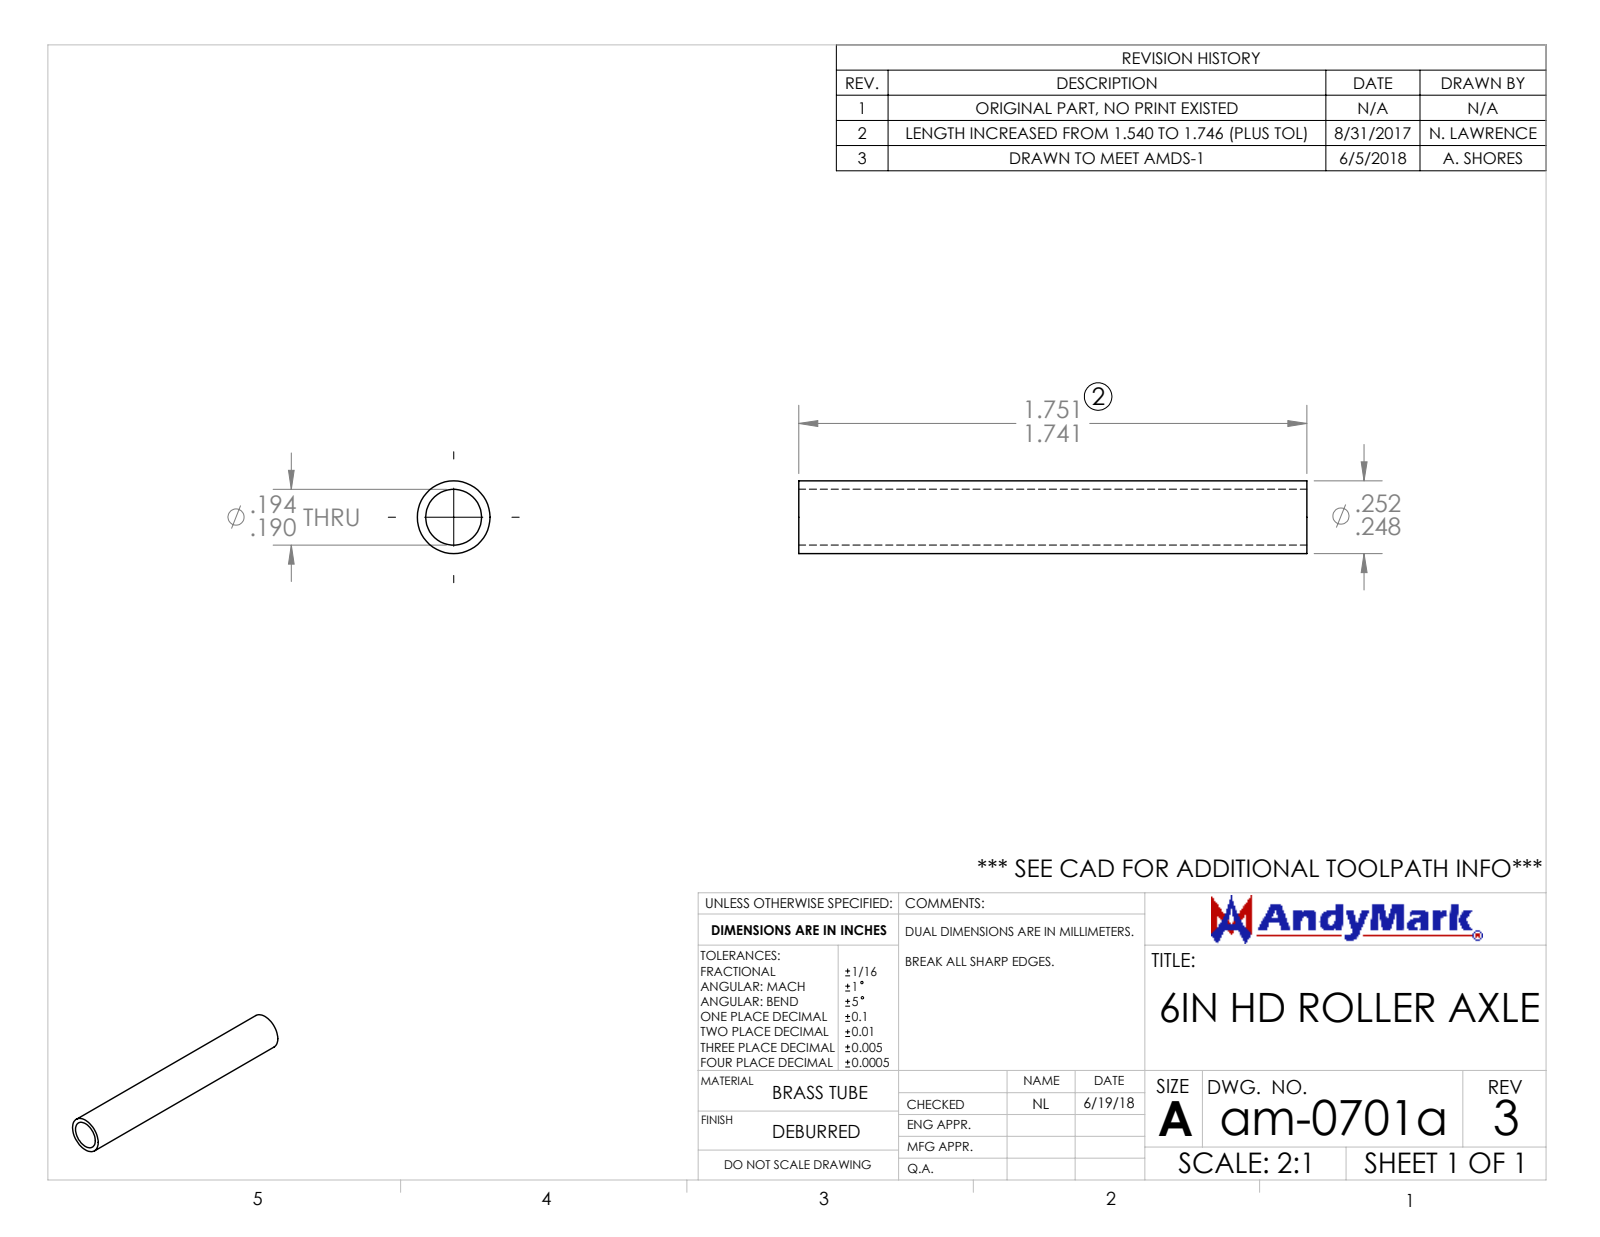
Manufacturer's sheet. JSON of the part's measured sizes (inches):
{"part_name": "am-0701a 6IN HD Roller Axle REV3", "step_written_by": "SolidWorks 2017 (AUTOMOTIVE_DESIGN)", "units": "inches", "bodies": {"solids": 1, "faces": 6, "planar": 2, "cylindrical": 4, "other": 0}, "overall_size": [1.746, 0.25, 0.25], "volume_in3": 0.035, "surface_area_in2": 2.465, "round_holes": [[0.192, 1]], "round_bosses_or_shafts": [[0.25, 1]], "face_to_face_distances": [1.746]}
